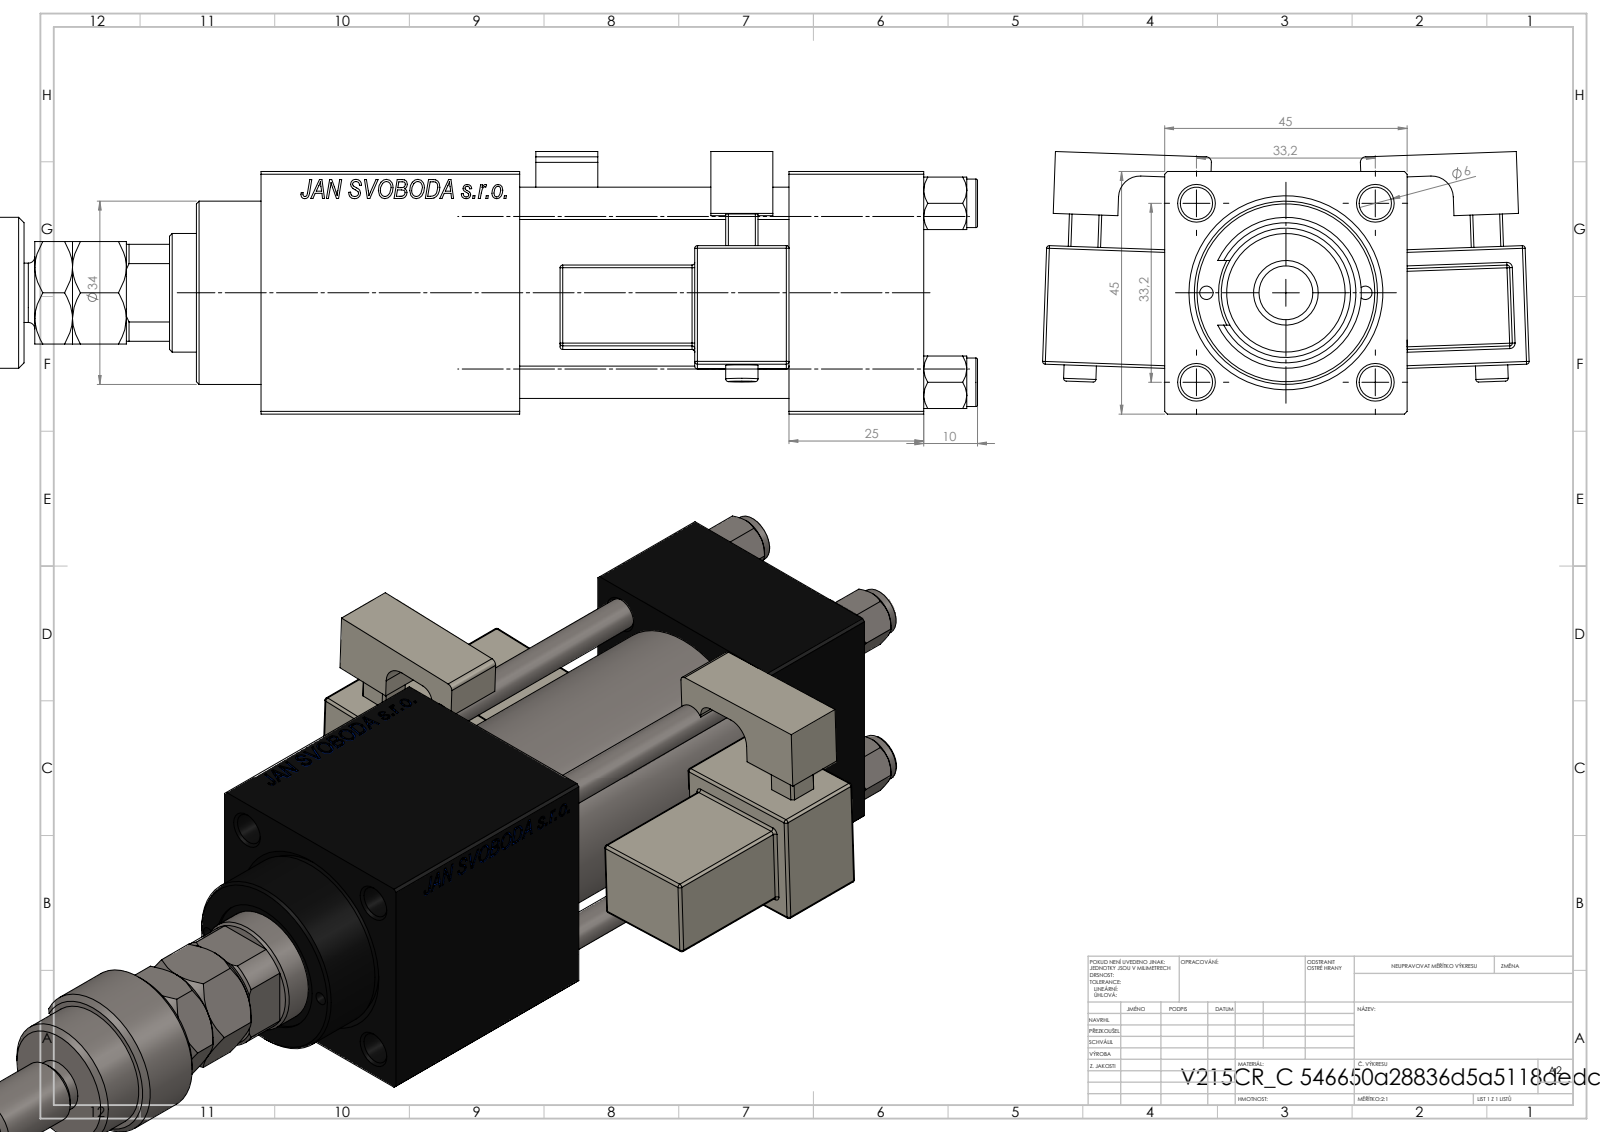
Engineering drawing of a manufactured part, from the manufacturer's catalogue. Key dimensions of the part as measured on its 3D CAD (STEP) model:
Part name (STEP PRODUCT): V215CR_MSU; V215CR_C_TYCINKA; NUT_M5_C; V215CR_VCP_C (+3 more)
STEP written by: SolidWorks 2019 (CONFIG_CONTROL_DESIGN)
Units: millimetres
Bodies: 14 solids, 1344 faces (601 planar, 159 cylindrical, 584 other)
Overall size (bounding box): 200 × 90.31 × 48.72
Volume: 260 162 mm³ · Surface area: 87 994 mm²
Round holes (diameter × count): ⌀6 ×4, ⌀2.5 ×2, ⌀7 ×2, ⌀13.16 ×2, ⌀20 ×2, ⌀10.5 ×1, ⌀22 ×1, ⌀24 ×1, ⌀25 ×1, ⌀32 ×1, ⌀33 ×1
Round bosses / shafts (diameter × count): ⌀9 ×4, ⌀6 ×2, ⌀38 ×1, ⌀34 ×1, ⌀28 ×1, ⌀12 ×1, ⌀10 ×1
Partial cylindrical surfaces — rounded edges, fillets, slot ends (radius × count): R0.5 ×48, R1 ×2, R2.5 ×2, R4 ×2, R9.75 ×1, R10.5 ×1
Main face-to-face distances: 45, 25, 3, 75, 50, 123, 22.99, 98, 14.5, 32.5
Hole centre spacings: 16.7, 23.48, 33.2, 35.47, 14.75, 46.95, 29.5, 75.5
